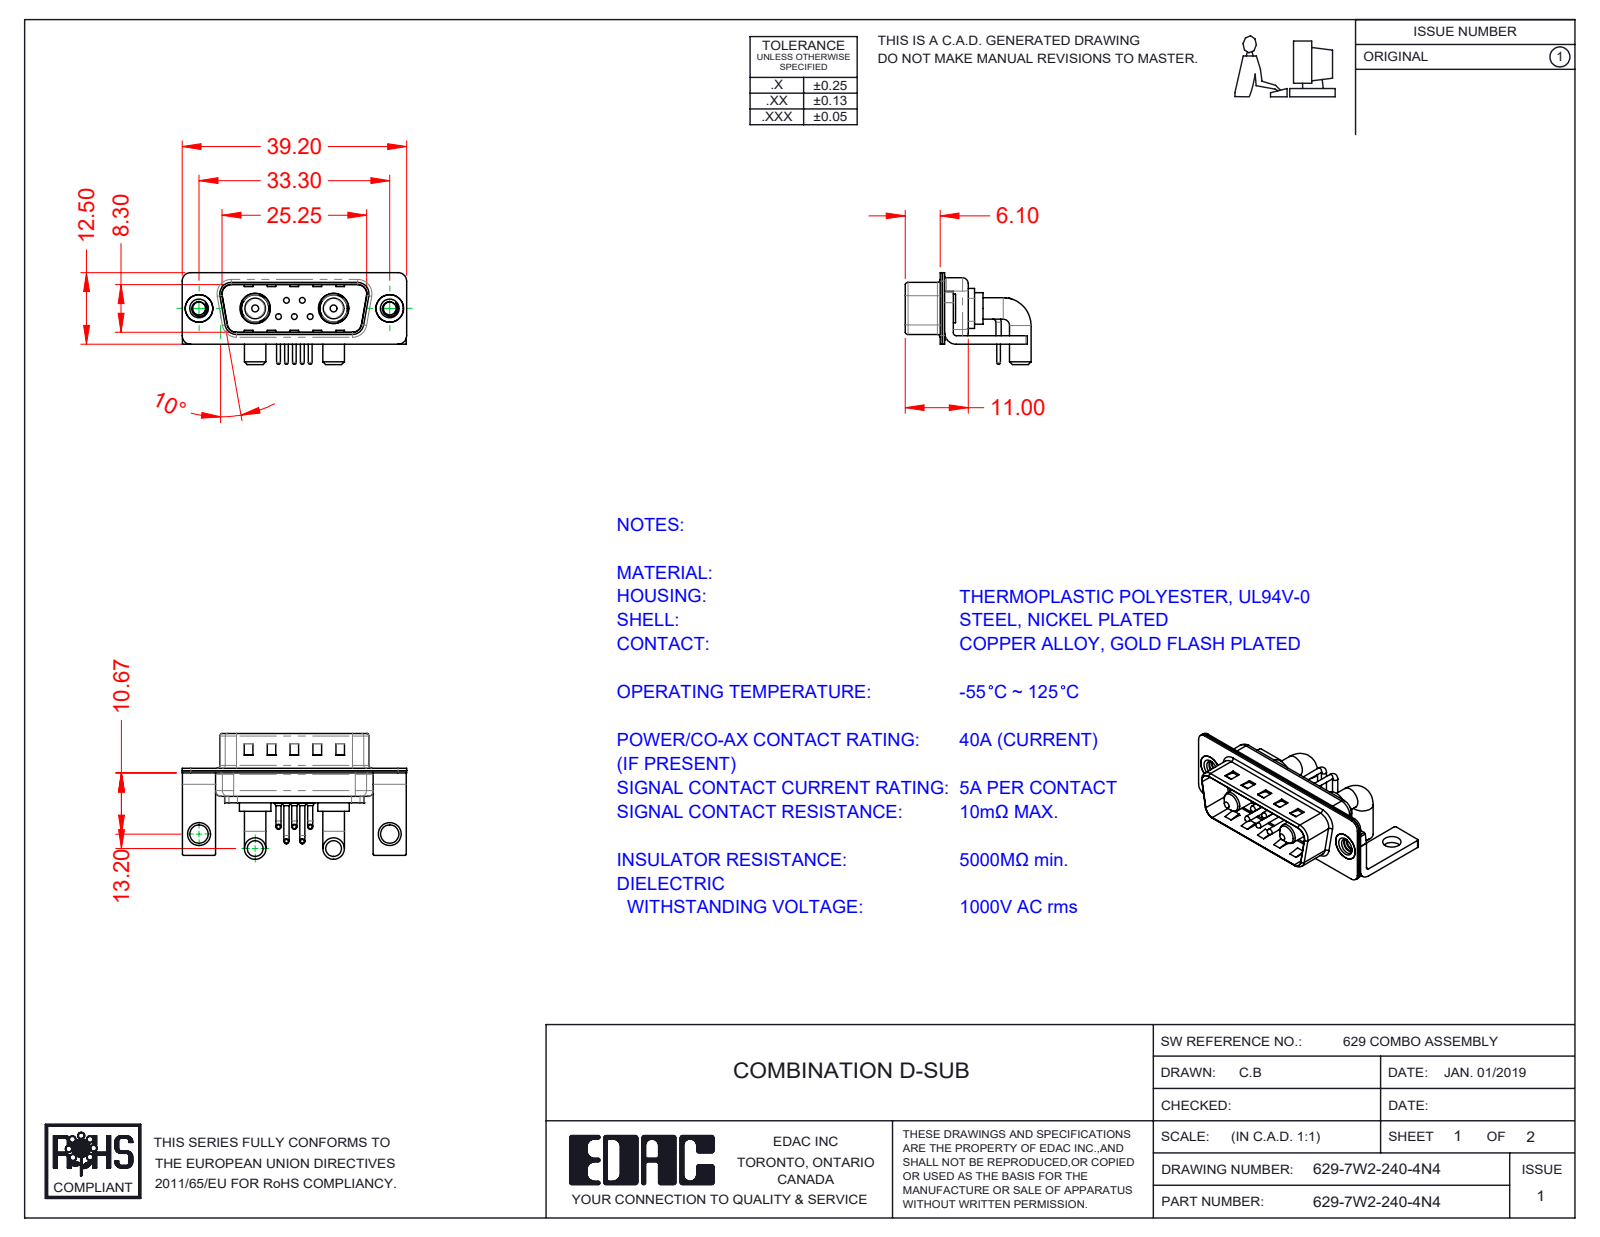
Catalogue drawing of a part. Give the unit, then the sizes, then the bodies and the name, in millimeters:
Units: millimetres
Overall size (bounding box): 39.2 × 21.98 × 16.05
Round holes (diameter × count): ⌀0.75 ×5, ⌀1.6 ×5, ⌀2 ×5, ⌀2.26 ×2, ⌀3.2 ×2, ⌀4 ×2, ⌀4.8 ×2, ⌀4.85 ×2, ⌀5.3 ×2
Round bosses / shafts (diameter × count): ⌀0.9 ×10, ⌀1.5 ×5, ⌀1 ×5, ⌀0.65 ×5, ⌀3.75 ×4, ⌀5.5 ×2, ⌀5.2 ×2, ⌀5 ×2
Partial cylindrical surfaces — rounded edges, fillets, slot ends (radius × count): R0.25 ×16, R1.5 ×16, R2 ×13, R0.5 ×9, R1.6 ×8, R1.01 ×5, R0.6 ×4, R0.65 ×4
Main face-to-face distances: 0.4, 0.8, 1.5, 9.5, 9.1, 8.7, 9.9, 0.6, 5.2, 0.75
Hole centre spacings: 3.16, 2.77, 9.8, 23.5, 33.3, 4.31, 4.33, 5.03
Volume: 2 568 mm³ · Surface area: 5 769 mm²
Bodies: 16 solids, 1016 faces (499 planar, 373 cylindrical, 144 other)
Part name (STEP PRODUCT): 629Combo Contact Row 2; 629Combo Housing_7W2; 629Combo Contact Row 1; 629Combo Shell Rear_15 Contacts (+5 more)
STEP written by: SolidWorks 2020 (CONFIG_CONTROL_DESIGN)
